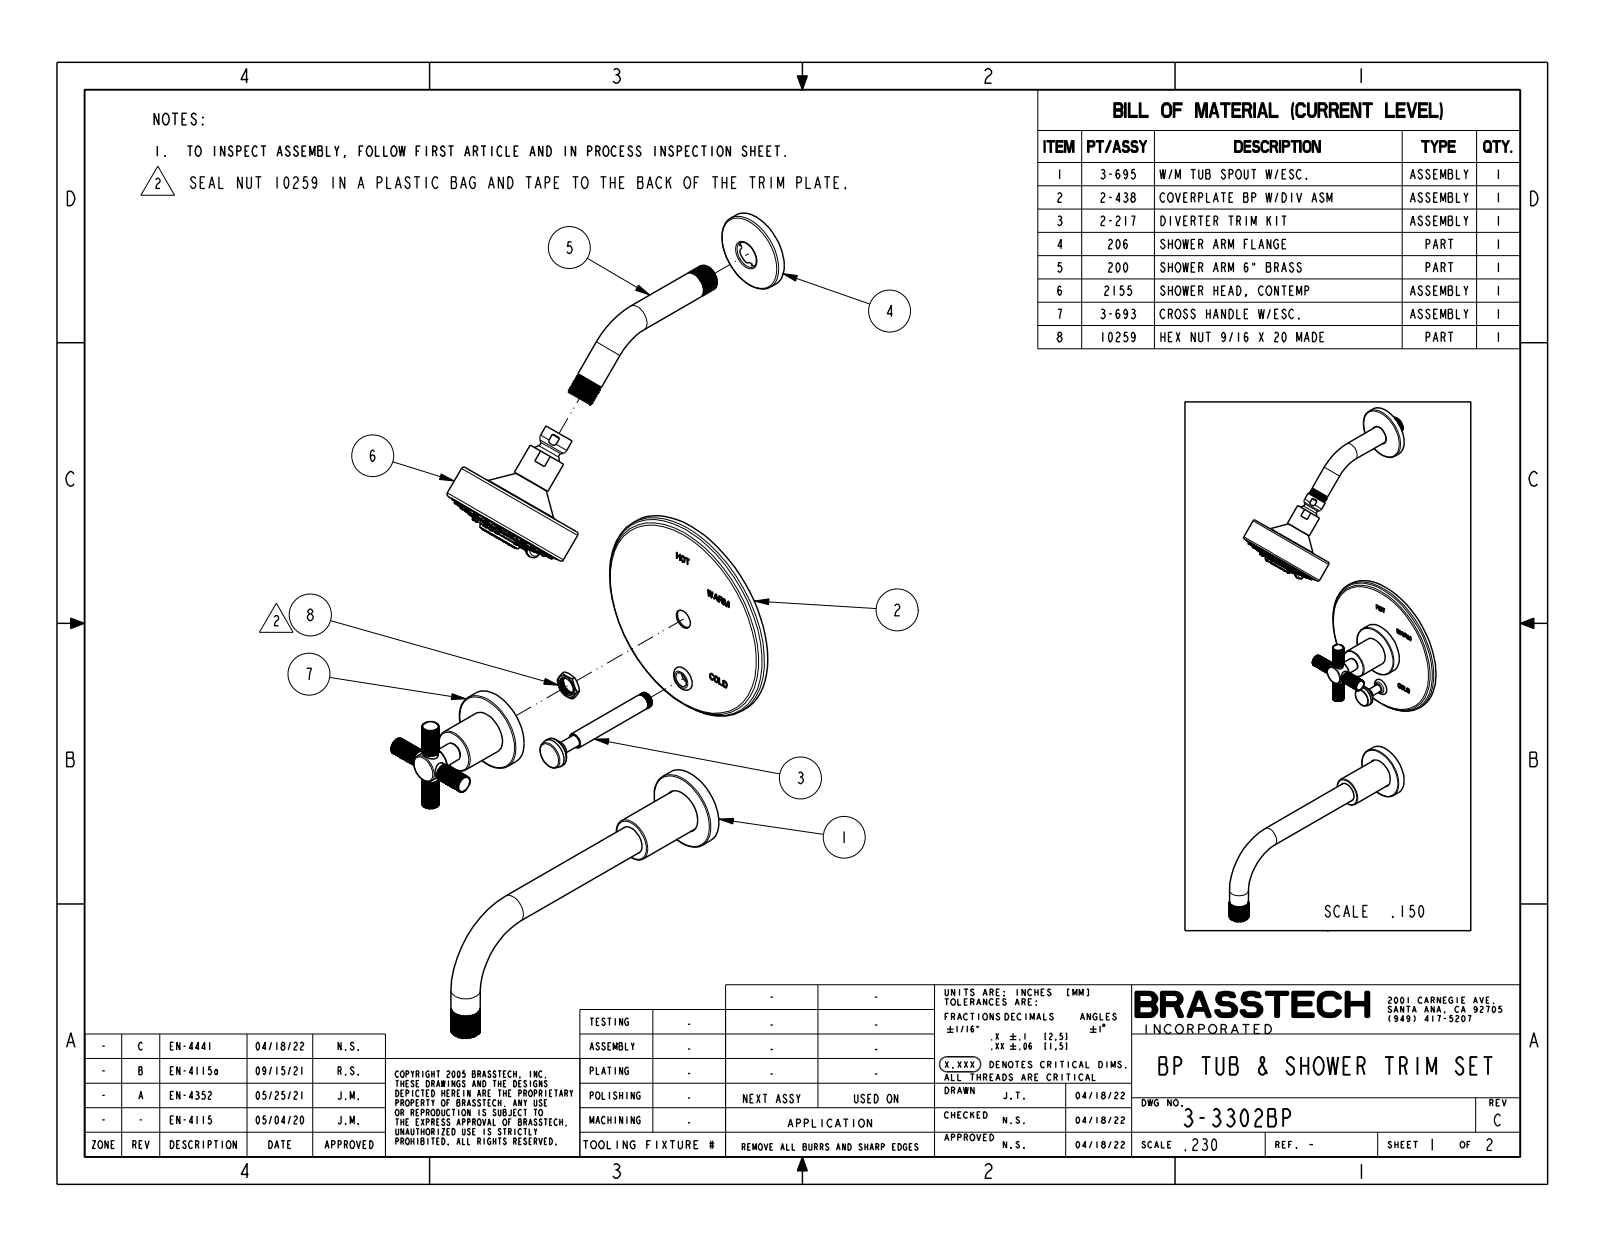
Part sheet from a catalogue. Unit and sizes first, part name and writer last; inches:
Units: inches
Overall size (bounding box): 23.63 × 9.938 × 6.5
Round holes (diameter × count): ⌀0.059 ×8, ⌀0.465 ×2, ⌀0.118 ×1, ⌀0.394 ×1, ⌀0.583 ×1, ⌀0.606 ×1, ⌀0.691 ×1, ⌀2.331 ×1
Round bosses / shafts (diameter × count): ⌀0.142 ×39, ⌀0.165 ×23, ⌀2.375 ×2, ⌀0.875 ×2, ⌀0.813 ×2, ⌀0.5 ×2, ⌀0.44 ×2, ⌀6.5 ×1
Partial cylindrical surfaces — rounded edges, fillets, slot ends (radius × count): R0.02 ×4, R0.138 ×1, R0.3 ×1, R0.472 ×1, R0.512 ×1
Main face-to-face distances: 0.313, 0.688, 0.375, 0.062, 0.375, 0.313, 2.088, 1.775, 1.713, 1.4
Hole centre spacings: 0.443, 0.579, 0.818, 0.819, 1.069, 0.443, 1.069, 1.07
Volume: 46.14 in³ · Surface area: 218.1 in²
Bodies: 3 solids, 17039 faces (560 planar, 3217 cylindrical, 13262 other)
Part name (STEP PRODUCT): 3-3302BP
STEP written by: CREO PARAMETRIC BY PTC INC, 2018400 (CONFIG_CONTROL_DESIGN)
